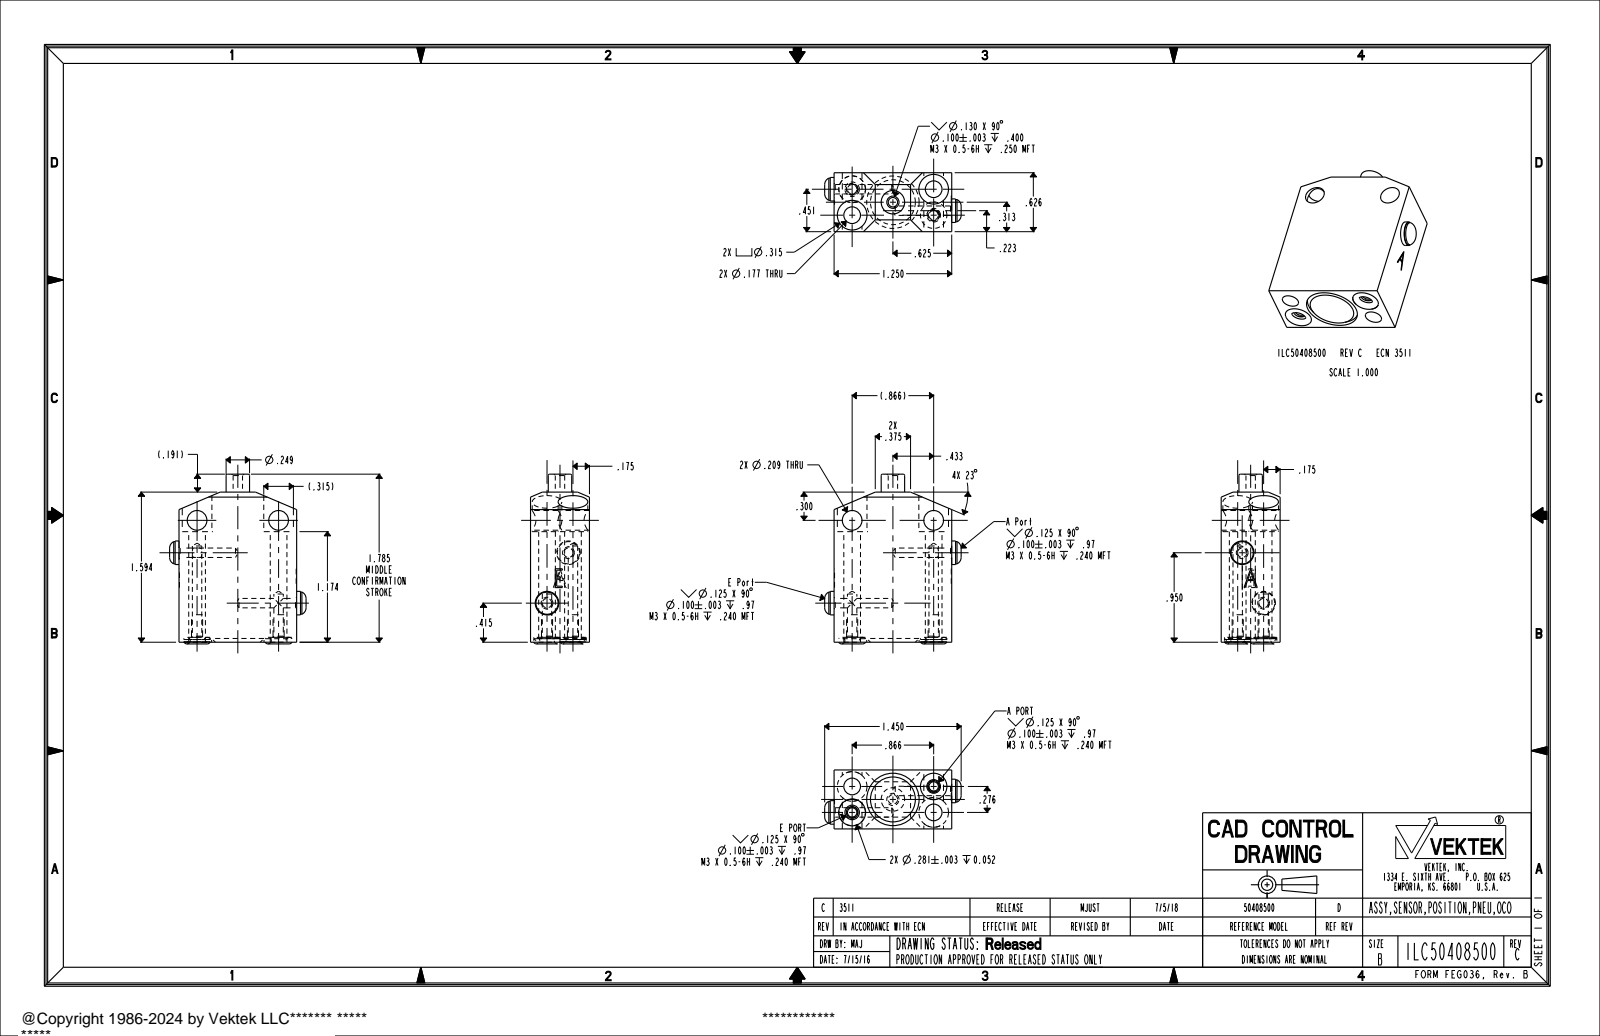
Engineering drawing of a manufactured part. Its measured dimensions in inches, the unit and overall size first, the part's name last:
Units: inches
Overall size (bounding box): 1.803 × 1.45 × 0.626
Round holes (diameter × count): ⌀0.1 ×5, ⌀0.177 ×2, ⌀0.209 ×2, ⌀0.281 ×2, ⌀0.315 ×2, ⌀0.557 ×1
Round bosses / shafts (diameter × count): ⌀0.25 ×2, ⌀0.118 ×2, ⌀0.249 ×1, ⌀0.236 ×1, ⌀0.236 ×1
Main face-to-face distances: 0.626, 1.25, 1.174, 0.42, 1.594, 1.542, 1.122, 0.052, 0.191, 0.611
Hole centre spacings: 0.454, 0.866, 0.276, 0.909, 0.581
Volume: 1.057 in³ · Surface area: 10.84 in²
Bodies: 1 solid, 134 faces (50 planar, 54 cylindrical, 30 other)
Part name (STEP PRODUCT): ILC50408500
STEP written by: PRO/ENGINEER BY PARAMETRIC TECHNOLOGY CORPORATION, 2013320 (AUTOMOTIVE_DESIGN)
